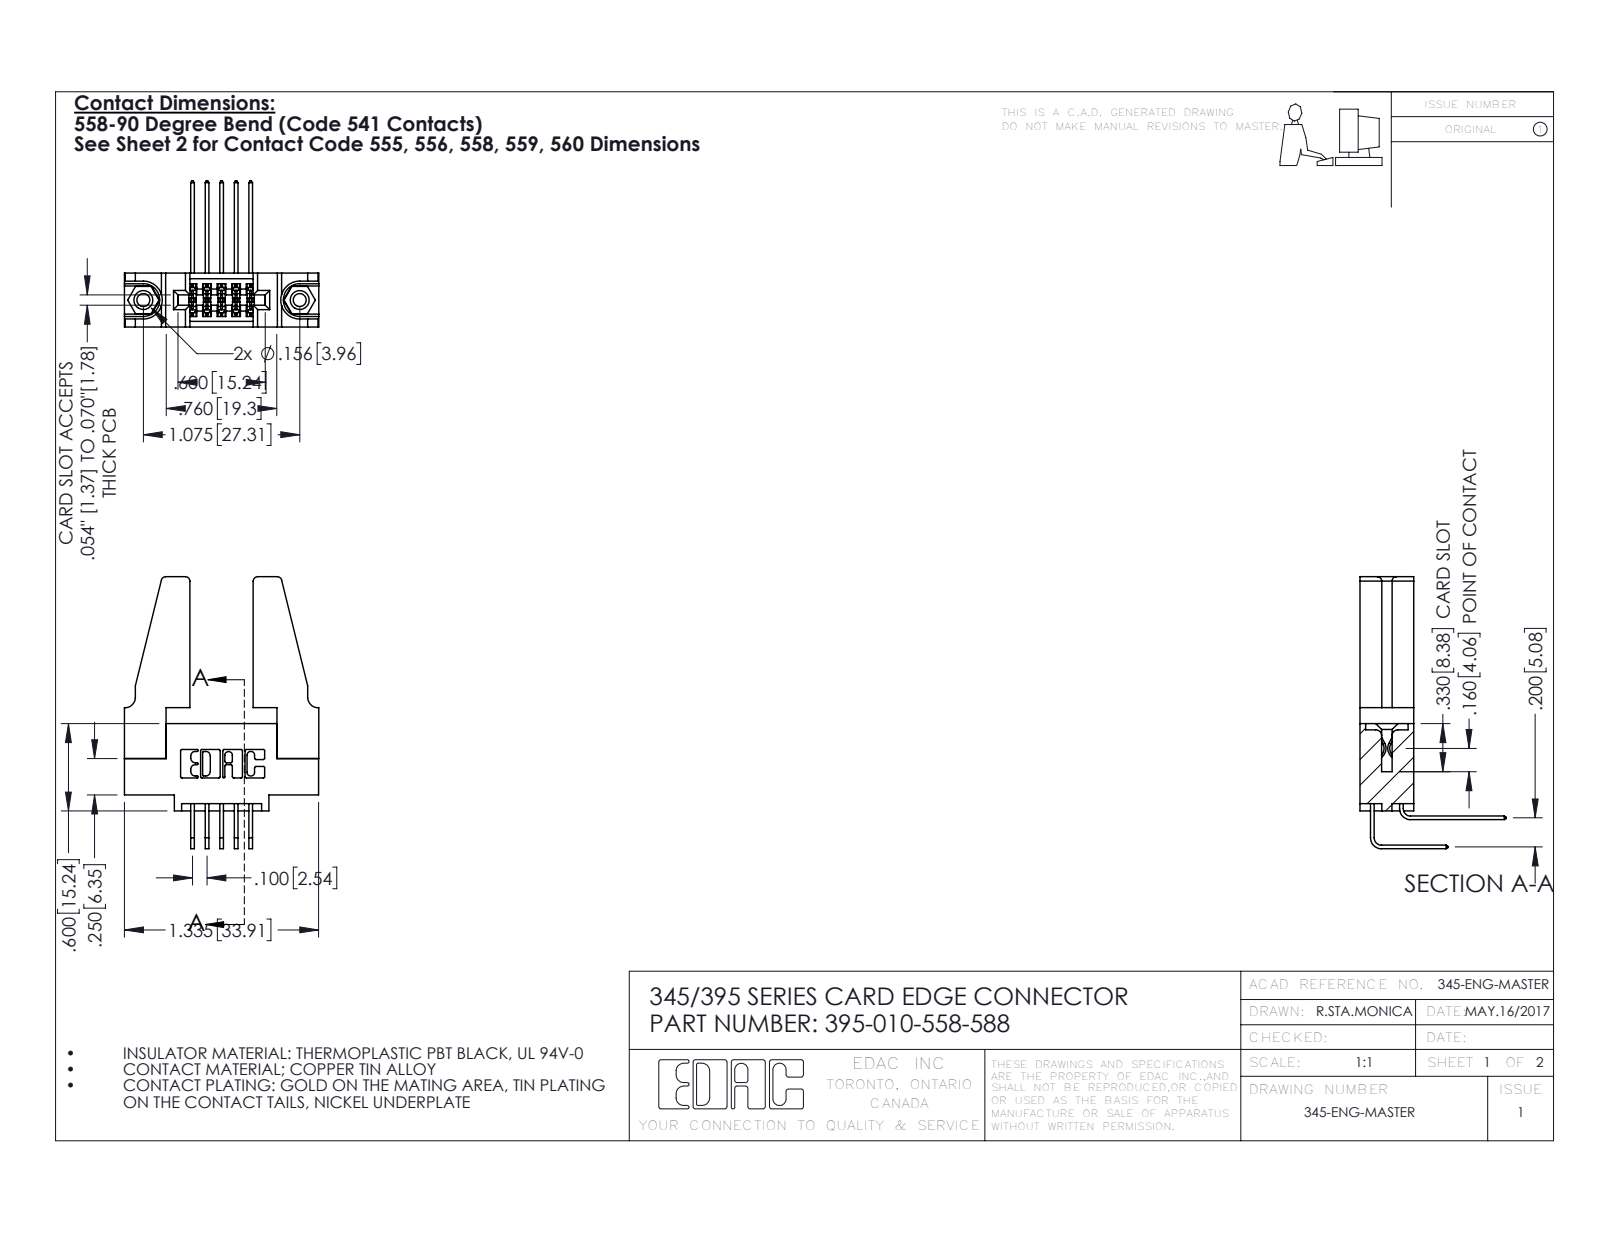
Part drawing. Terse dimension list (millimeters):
name: 395-010-558-588; 345-292-001_558 559 Tail - 1; 345 Part_0.110 Offset - 0.156 Dia-TH; 345-292-001_558 Tail - 2 (+2 more)
written by: SolidWorks 2016 (CONFIG_CONTROL_DESIGN)
unit: mm
bodies: 15 solids, 774 faces (506 planar, 252 cylindrical, 16 other)
size: 47.5 × 33.9 × 25.5
volume: 6 190 mm³; area: 7 110 mm²
holes: 2× ⌀2.3, 2× ⌀3.2, 2× ⌀4, 1× ⌀1.6
bosses: 2× ⌀3.9
rounds: 22× R0.3, 16× R0.2, 8× R0.8, 6× R0.2, 6× R0.8, 3× R0.7, 2× R0.4, 2× R0.5
face distances: 9.4, 1.8, 7.6, 5.1, 3.8, 3.8, 5.6, 2, 2.5, 6.9
hole spacings: 6.9, 21.5, 27.3
